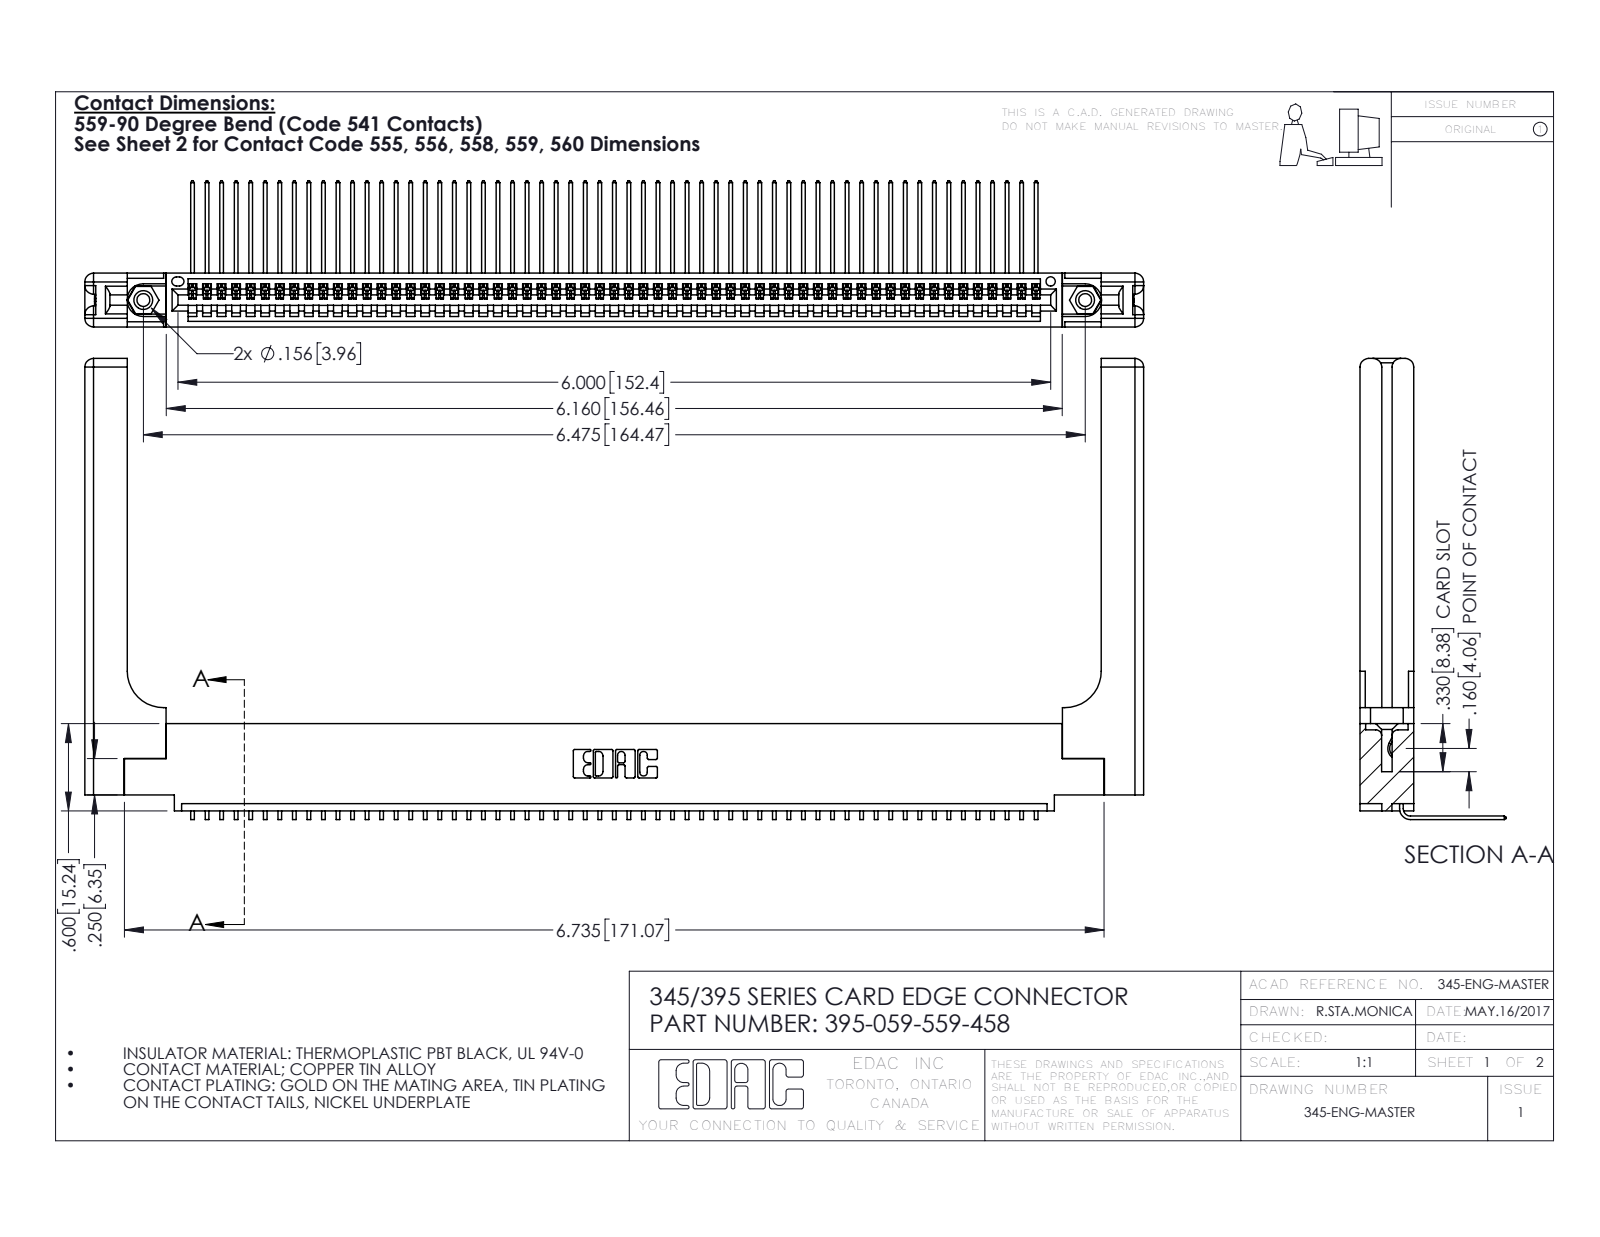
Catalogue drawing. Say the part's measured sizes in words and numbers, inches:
The part is named "345-292-001_558 559 Tail - 1; 395-059-559-458; 345-250-001_345-250-001-102; 345-220-058_345-220-058 (+1 more)". Its 3-D file was written by "SolidWorks 2016 (CONFIG_CONTROL_DESIGN)". It is 64 solids with 3926 faces: 2710 planar, 1156 cylindrical and 60 other. Overall it measures 7.279 by 3.169 by 1.005 inches. Its volume is 1.607 cubic inches and its surface area 47.21 square inches. Round holes: 2 of diameter 0.089, 2 of diameter 0.125, 2 of diameter 0.156, 1 of diameter 0.064. Round bosses or shafts: 2 of diameter 0.155. Partial cylindrical surfaces (rounded edges, fillets, slot ends): 118 of radius 0.006, 22 of radius 0.01, 16 of radius 0.06, 6 of radius 0.007, 6 of radius 0.031, 3 of radius 0.026, 2 of radius 0.03, 2 of radius 0.031. The main face-to-face distances are 0.072, 0.37, 0.298, 0.098, 0.272, 0.025, 0.2, 0.225, 0.148, 0.15. The hole center spacings are 0.27, 6.239, 6.475.
